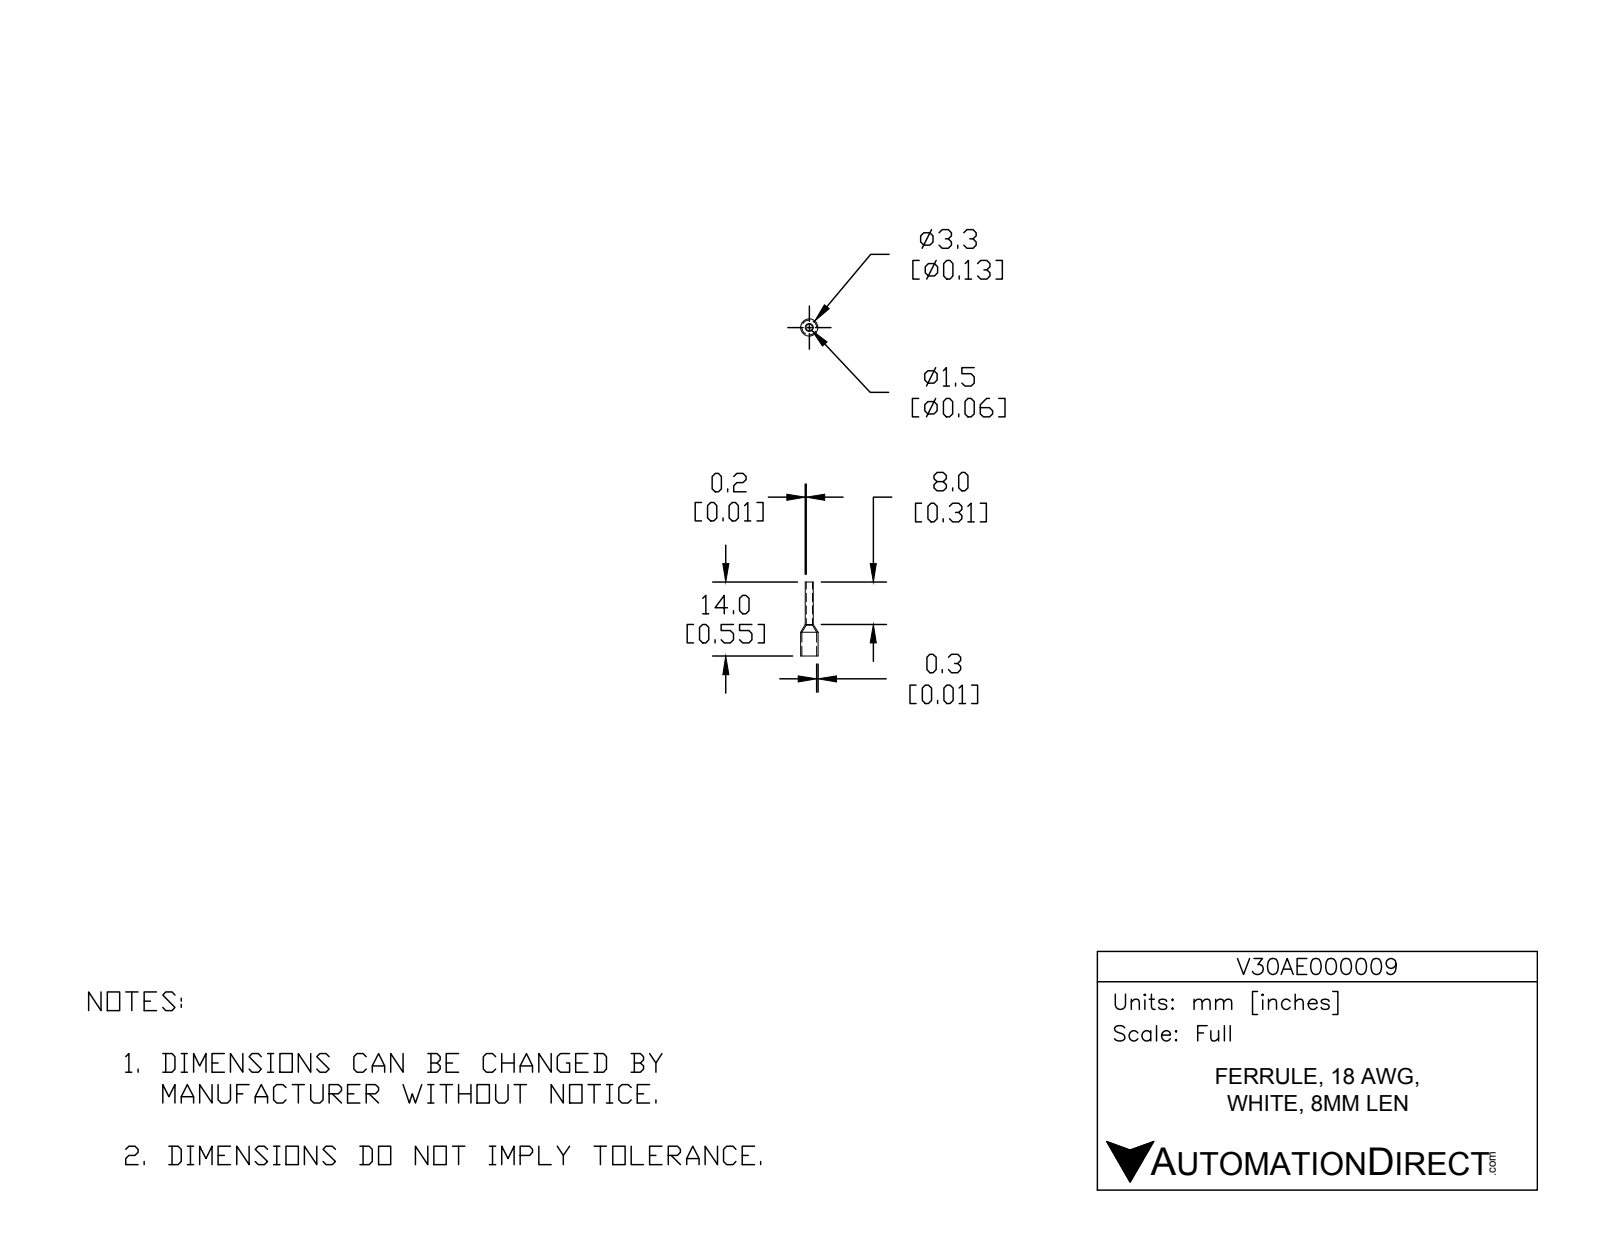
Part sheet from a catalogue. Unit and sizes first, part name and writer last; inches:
Units: inches
Overall size (bounding box): 0.551 × 0.13 × 0.13
Round holes (diameter × count): ⌀0.047 ×1, ⌀0.11 ×1
Round bosses / shafts (diameter × count): ⌀0.13 ×1, ⌀0.059 ×1
Main face-to-face distances: 0.551
Volume: 0.001 in³ · Surface area: 0.281 in²
Bodies: 1 solid, 14 faces (2 planar, 8 cylindrical, 4 other)
Part name (STEP PRODUCT): V30AE000009
STEP written by: SolidWorks 2017 (AUTOMOTIVE_DESIGN)
